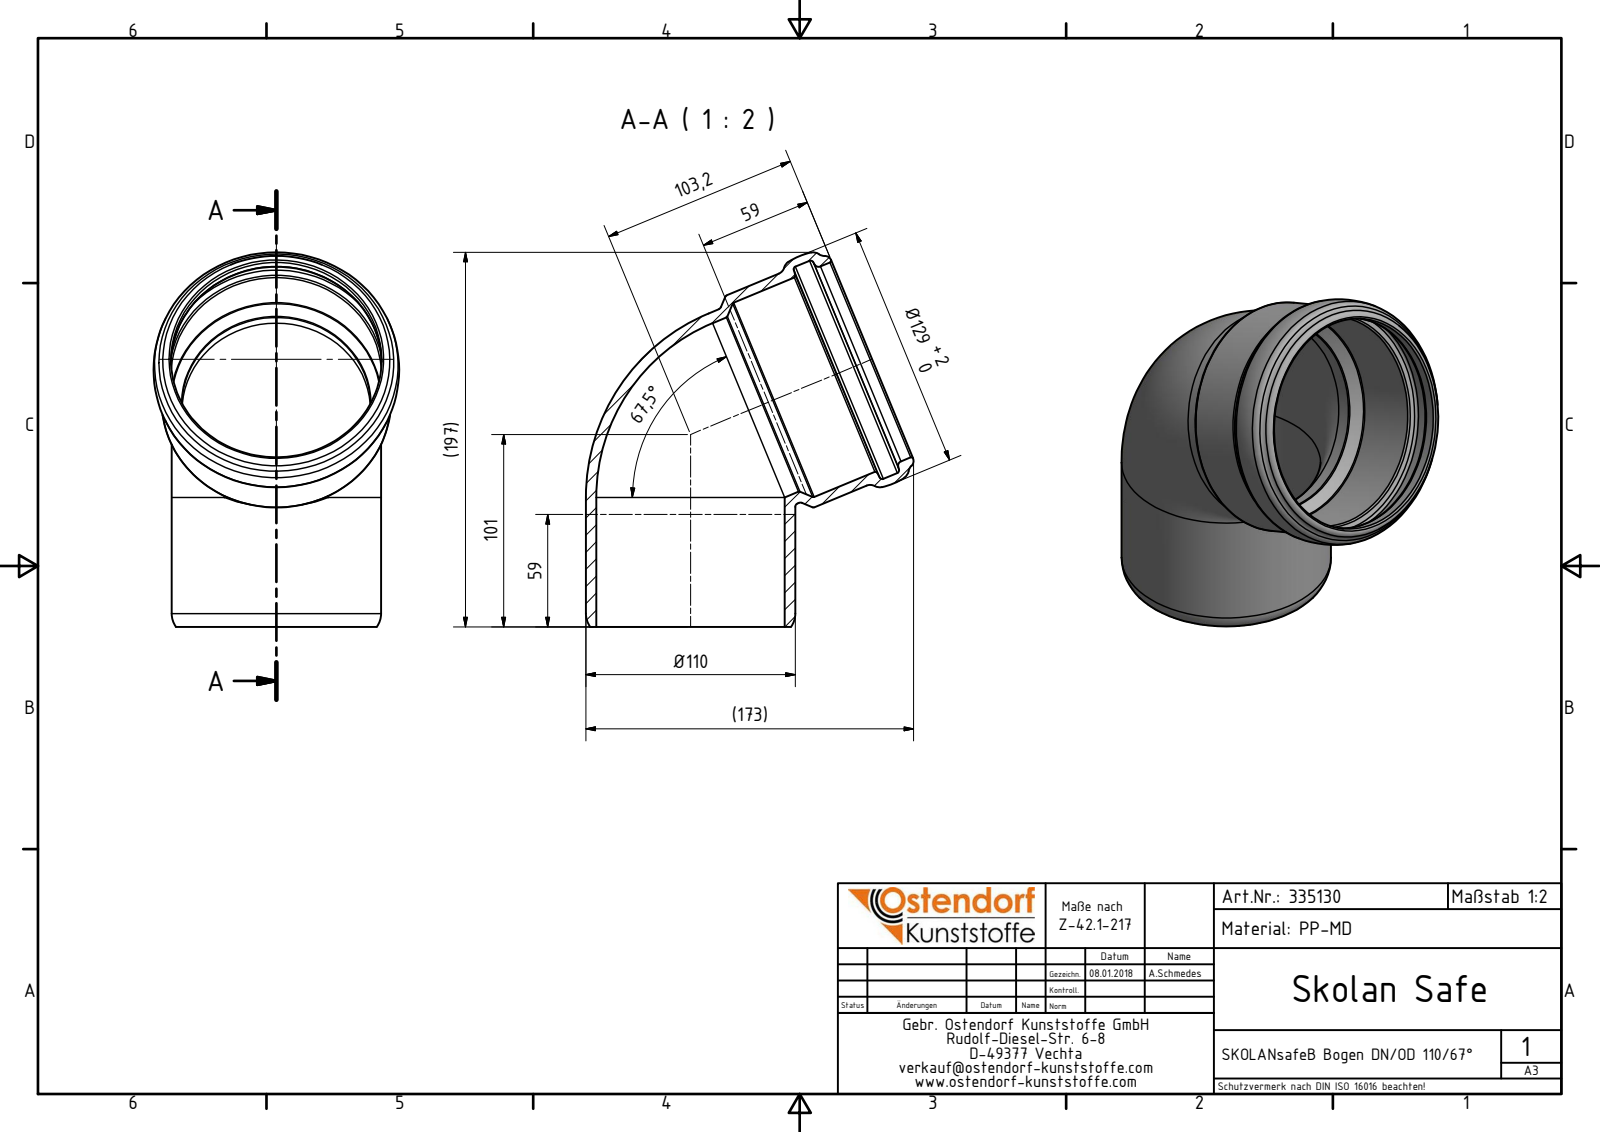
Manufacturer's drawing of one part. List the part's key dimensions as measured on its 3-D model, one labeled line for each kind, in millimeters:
Part name (STEP PRODUCT): 335130 SKOLANsafeB Bogen DN_OD 110_67°
STEP written by: Autodesk Inventor 2016 (AUTOMOTIVE_DESIGN)
Units: millimetres
Bodies: 1 solid, 32 faces (1 planar, 8 cylindrical, 23 other)
Overall size (bounding box): 196.59 × 172.18 × 129
Volume: 358 306 mm³ · Surface area: 141 088 mm²
Round holes (diameter × count): ⌀99 ×2, ⌀110.4 ×1, ⌀110.7 ×1, ⌀120.6 ×1
Round bosses / shafts (diameter × count): ⌀110 ×2, ⌀120.4 ×1
